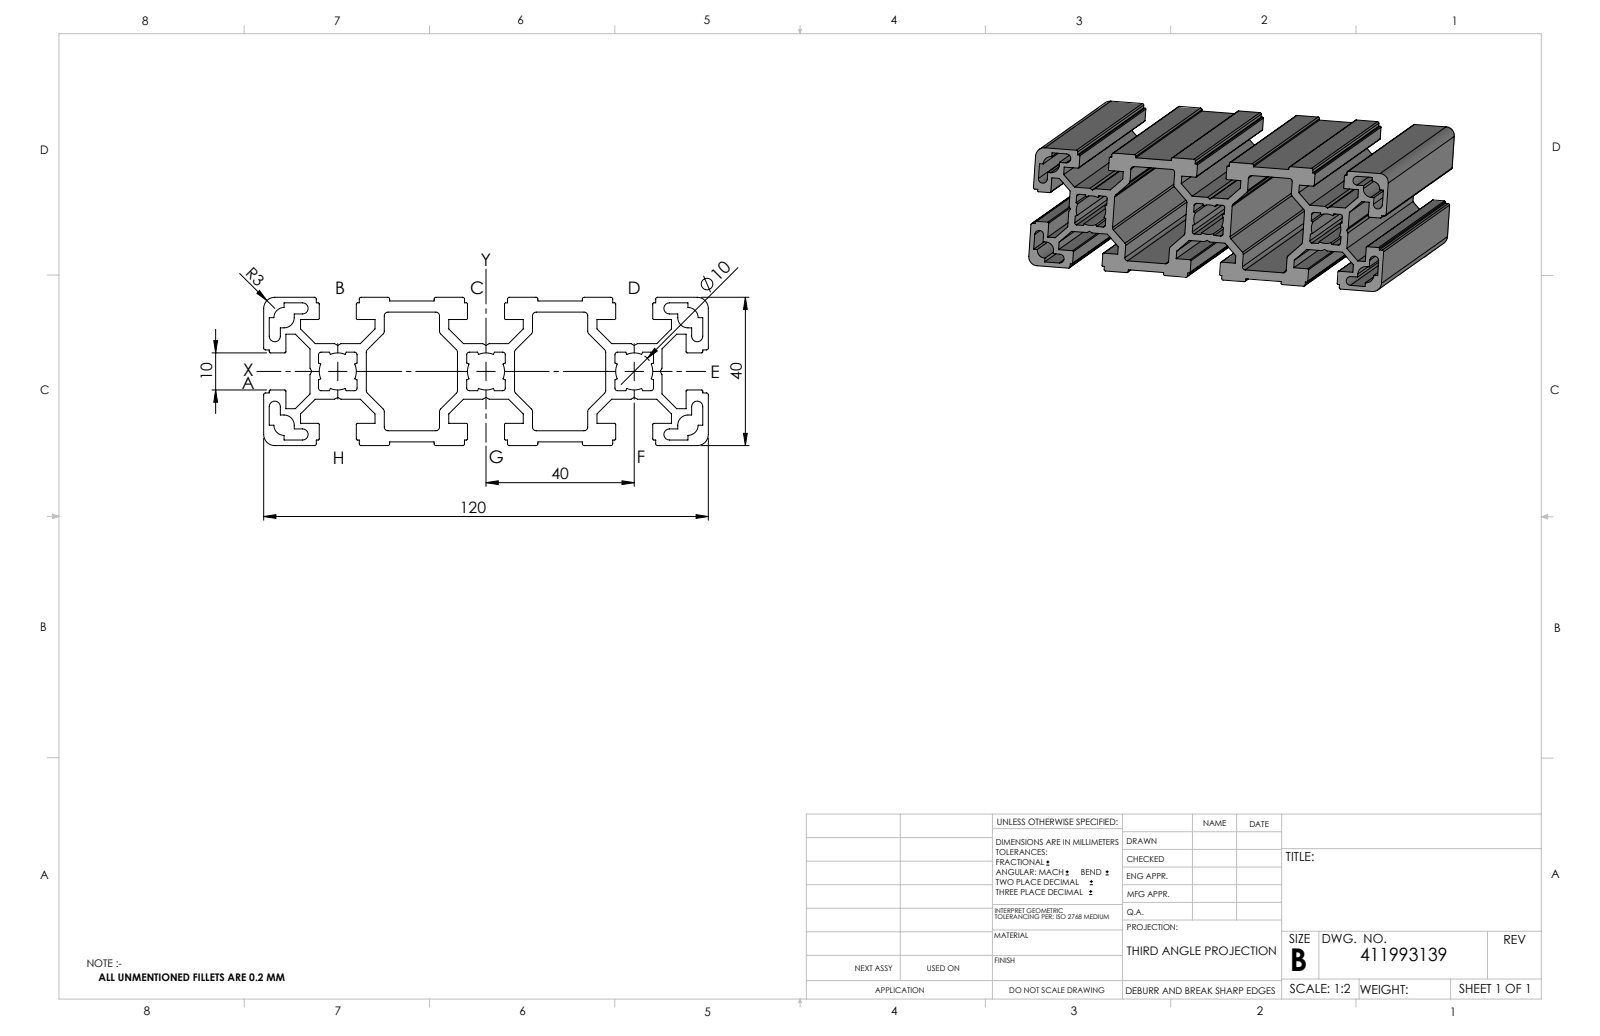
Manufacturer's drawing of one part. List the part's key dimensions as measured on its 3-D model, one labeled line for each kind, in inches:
Part name (STEP PRODUCT): 411993139_c_1
STEP written by: SolidWorks 2014 (CONFIG_CONTROL_DESIGN)
Units: inches
Bodies: 1 solid, 391 faces (262 planar, 129 cylindrical, 0 other)
Overall size (bounding box): 7.874 × 4.724 × 1.575
Volume: 18.73 in³ · Surface area: 352 in²
Partial cylindrical surfaces — rounded edges, fillets, slot ends (radius × count): R0.012 ×32, R0.02 ×24, R0.039 ×24, R0.028 ×12, R0.059 ×8, R0.108 ×4, R0.118 ×4, R0.197 ×3
Main face-to-face distances: 1.575, 0.492, 0.098, 0.079, 0.02, 0.236, 0.256, 0.925, 0.118, 1.113
